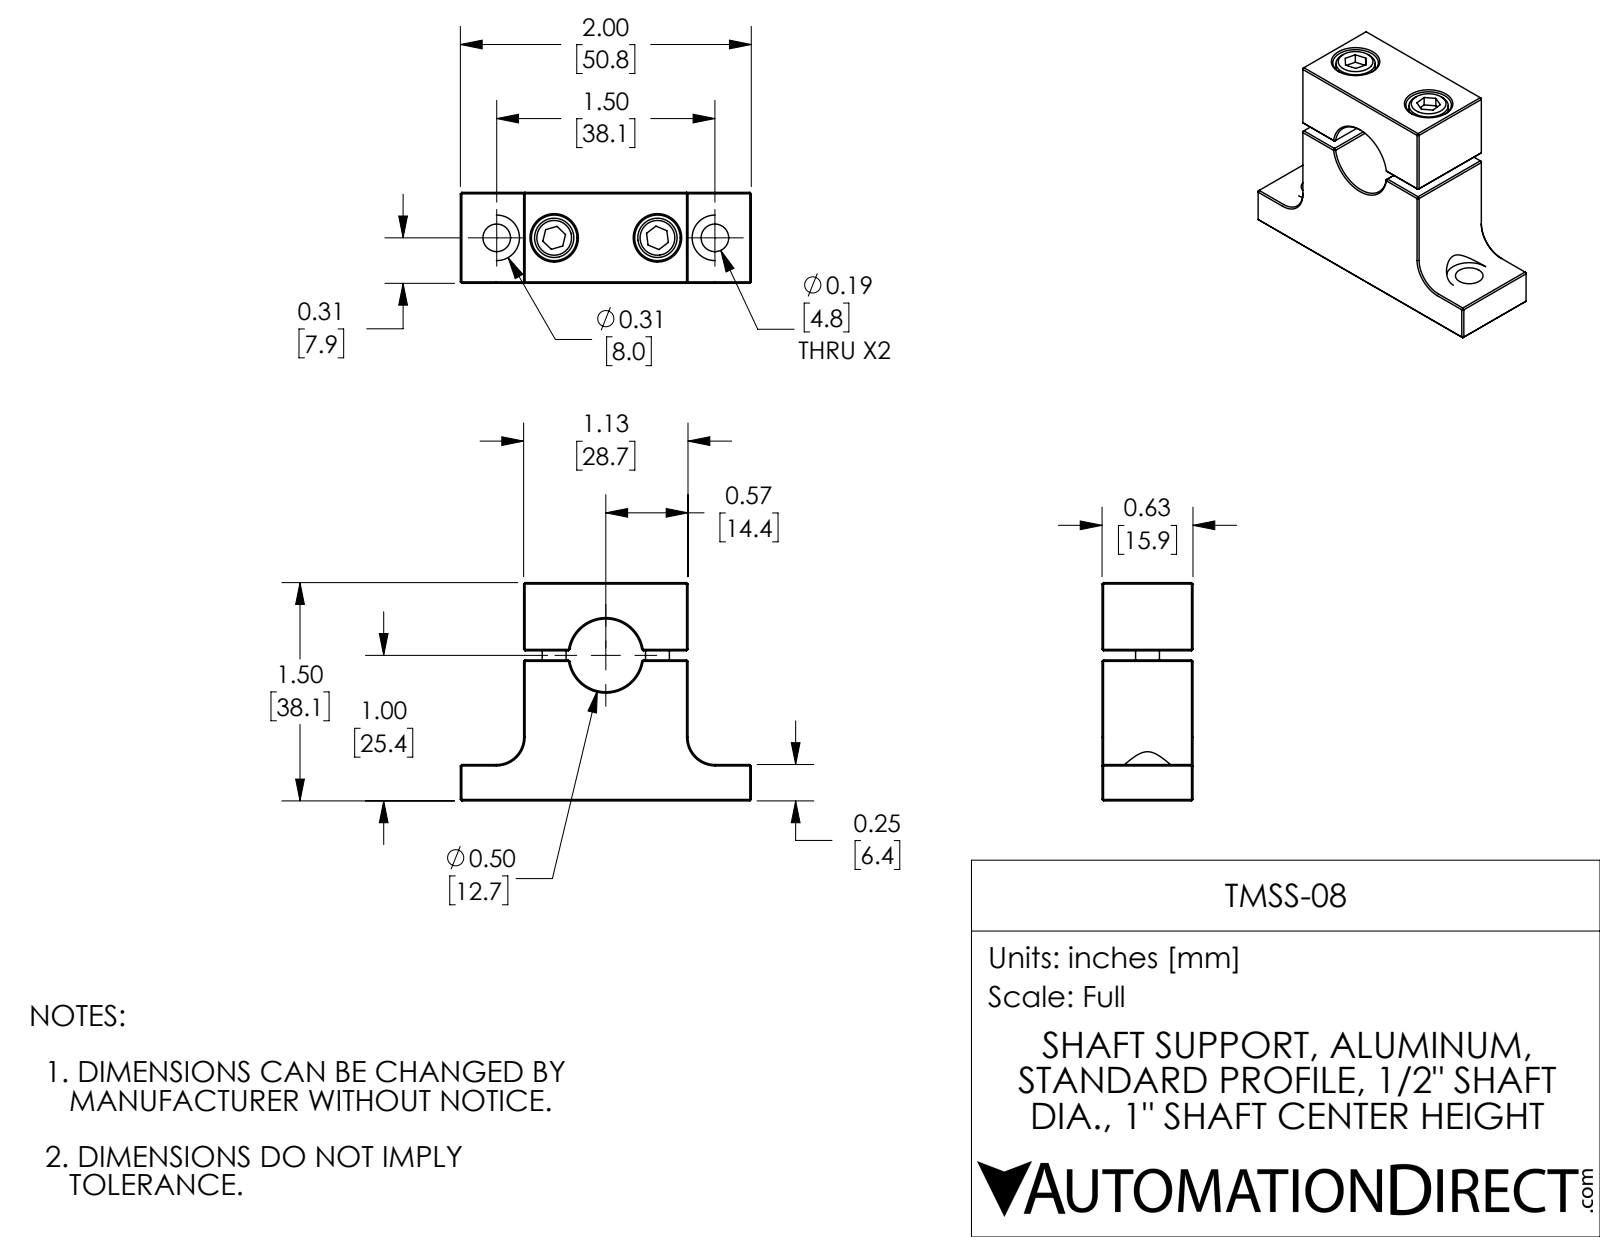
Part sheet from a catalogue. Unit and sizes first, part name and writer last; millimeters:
Units: millimetres
Overall size (bounding box): 50.8 × 38.1 × 15.9
Round holes (diameter × count): ⌀3.3 ×2, ⌀4.5 ×2, ⌀4.8 ×2, ⌀8 ×2, ⌀12.7 ×1
Round bosses / shafts (diameter × count): ⌀6.9 ×2, ⌀4.2 ×2
Partial cylindrical surfaces — rounded edges, fillets, slot ends (radius × count): R4 ×2, R4.7 ×2
Main face-to-face distances: 15.9, 28.7, 38.1, 24.6, 13.5, 26.2, 1.6, 11.9, 6.4, 18.3
Hole centre spacings: 10, 28.1, 18, 38.1
Volume: 16 670 mm³ · Surface area: 7 606 mm²
Bodies: 4 solids, 165 faces (110 planar, 31 cylindrical, 24 other)
Part name (STEP PRODUCT): TMSS-08
STEP written by: SolidWorks 2017 (AUTOMOTIVE_DESIGN)
